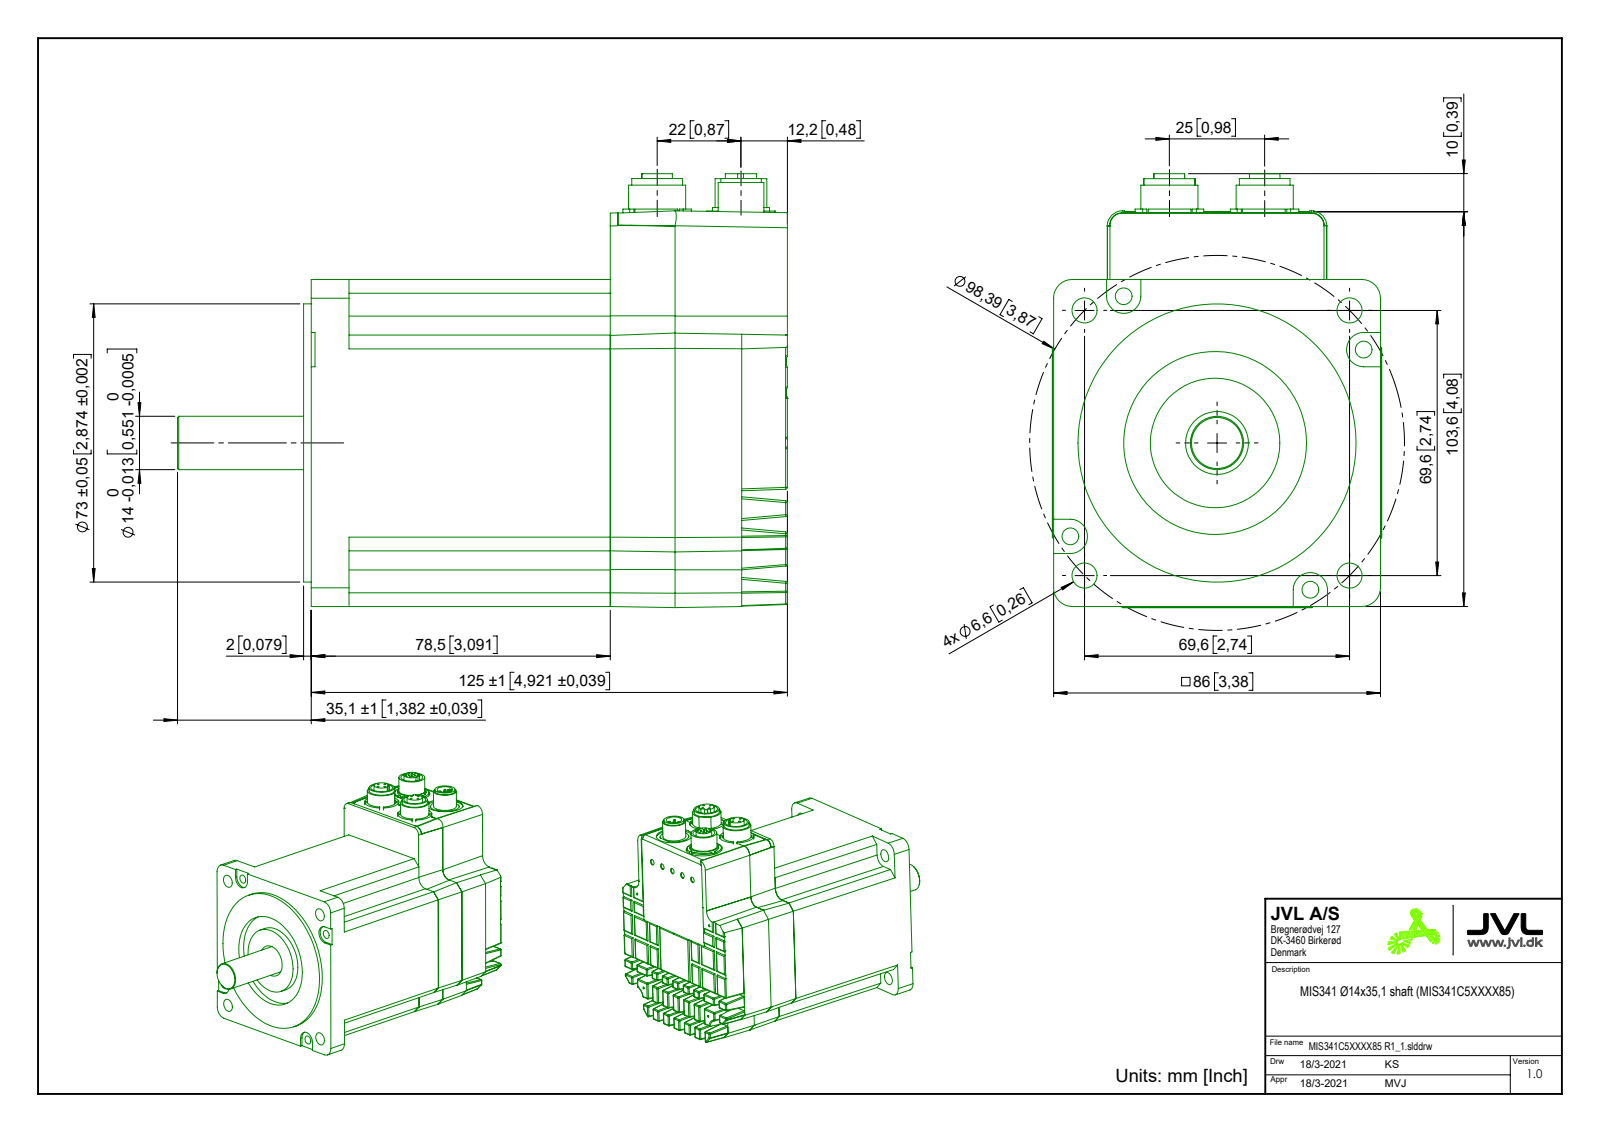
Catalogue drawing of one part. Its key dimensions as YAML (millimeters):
part_name: "MIS341C5XXXX85 R1_1"
step_written_by: "SolidWorks 2020 (AUTOMOTIVE_DESIGN)"
units: millimeters
bodies: {solids: 1, faces: 1085, planar: 431, cylindrical: 498, other: 156}
overall_size: [160.1, 113.87, 86.41]
volume: 861812
surface_area: 74963
round_holes:
  - {diameter: 0.7, count: 17}
  - {diameter: 1, count: 12}
  - {diameter: 3, count: 5}
  - {diameter: 4.3, count: 4}
  - {diameter: 4.4, count: 4}
  - {diameter: 6.6, count: 4}
  - {diameter: 11.5, count: 3}
  - {diameter: 19, count: 2}
  - {diameter: 8.2, count: 1}
  - {diameter: 16.5, count: 1}
  - {diameter: 48, count: 1}
round_bosses_or_shafts:
  - {diameter: 1, count: 5}
  - {diameter: 18, count: 3}
  - {diameter: 15, count: 3}
  - {diameter: 8.2, count: 3}
  - {diameter: 13.3, count: 2}
  - {diameter: 8, count: 2}
  - {diameter: 73, count: 1}
  - {diameter: 34, count: 1}
partial_cylinders:
  - {radius: 0.5, count: 164}
  - {radius: 4.5, count: 4}
  - {radius: 4.9, count: 4}
  - {radius: 5, count: 4}
  - {radius: 9.5, count: 4}
  - {radius: 0.48, count: 3}
  - {radius: 2, count: 3}
  - {radius: 7.5, count: 3}
face_to_face_distances: [85.8, 14.6, 71.2, 2, 127, 125, 126.75, 124.75, 56.6, 95.58]
hole_center_spacings: [3.25, 3.54, 1.65, 2.48, 3.23, 3.26, 8.4, 45.63]
